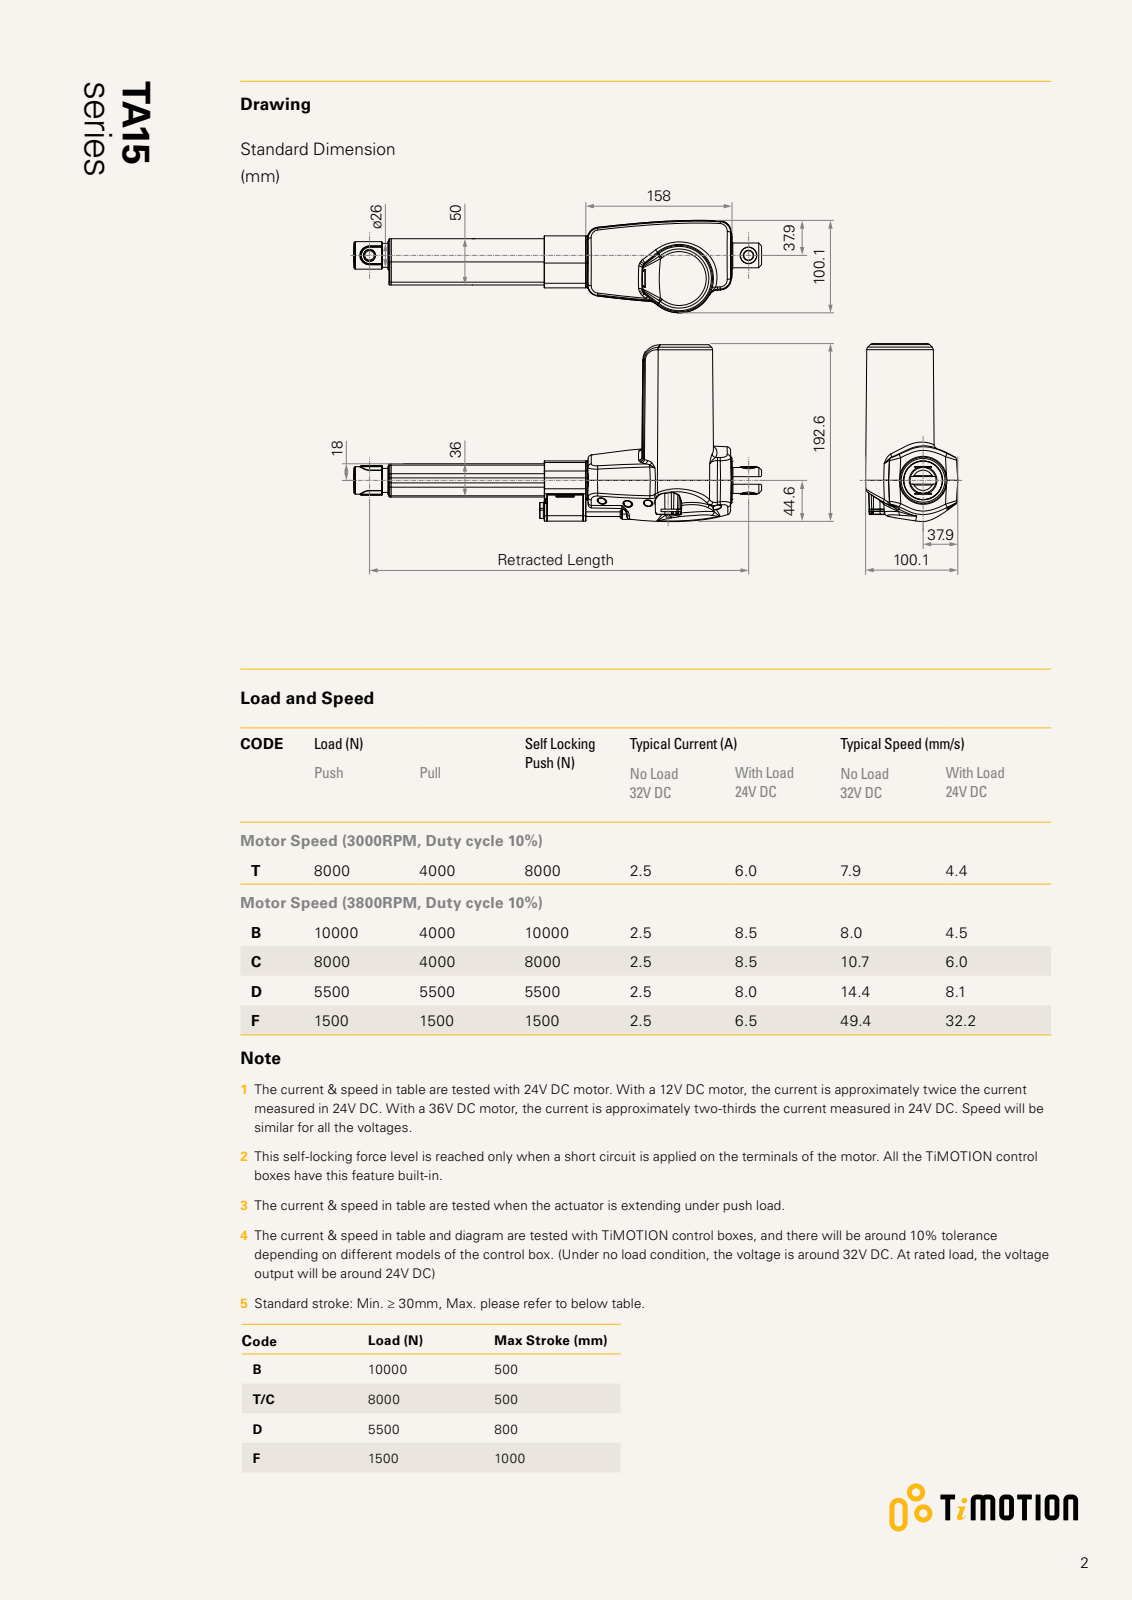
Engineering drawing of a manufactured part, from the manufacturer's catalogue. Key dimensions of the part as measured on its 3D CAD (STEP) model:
Part name (STEP PRODUCT): 3D-TA15
STEP written by: SolidWorks 2010 (CONFIG_CONTROL_DESIGN)
Units: millimetres
Bodies: 0 solids, 722 faces (149 planar, 190 cylindrical, 383 other)
Overall size (bounding box): 441.3 × 199.52 × 147.19
Round holes (diameter × count): ⌀4 ×2, ⌀12.2 ×2, ⌀2.2 ×1, ⌀7.5 ×1, ⌀12.5 ×1, ⌀42 ×1
Round bosses / shafts (diameter × count): ⌀6 ×2, ⌀29.7 ×1, ⌀28 ×1, ⌀26 ×1, ⌀21 ×1, ⌀16 ×1, ⌀9 ×1, ⌀5 ×1
Partial cylindrical surfaces — rounded edges, fillets, slot ends (radius × count): R0.3 ×23, R0.5 ×19, R1 ×15, R2 ×7, R4 ×5, R10 ×3, R1.5 ×2, R3 ×2
Main face-to-face distances: 3.1, 42, 3, 45, 39, 147.95, 45.99, 31, 36.09, 9.9
Hole centre spacings: 8.84, 36.99, 410, 12, 30, 30.07, 31.31, 32.24
